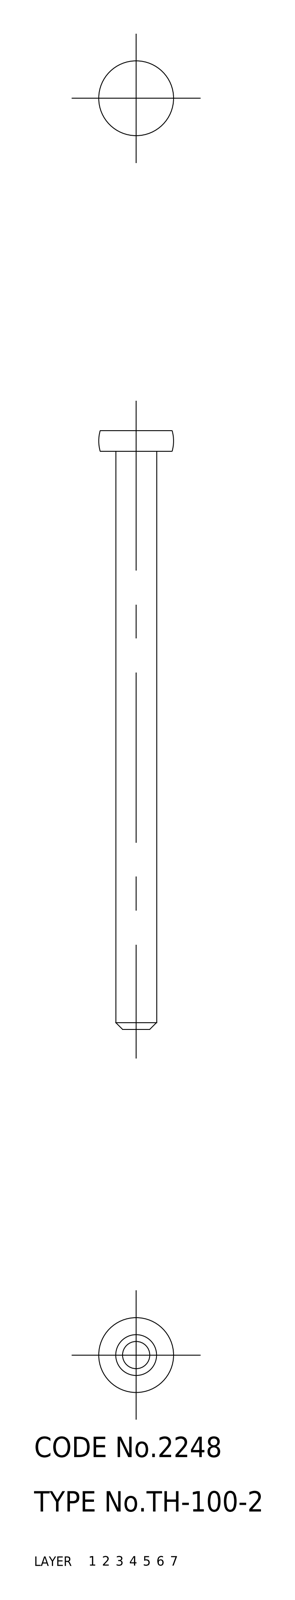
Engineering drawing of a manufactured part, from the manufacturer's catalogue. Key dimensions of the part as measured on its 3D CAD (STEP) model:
Part name (STEP PRODUCT): shaft
STEP written by: CADfix (AUTOMOTIVE_DESIGN)
Units: millimetres
Bodies: 1 solid, 8 faces (0 planar, 0 cylindrical, 8 other)
Overall size (bounding box): 88 × 11 × 11
Volume: 2 678 mm³ · Surface area: 1 870 mm²
